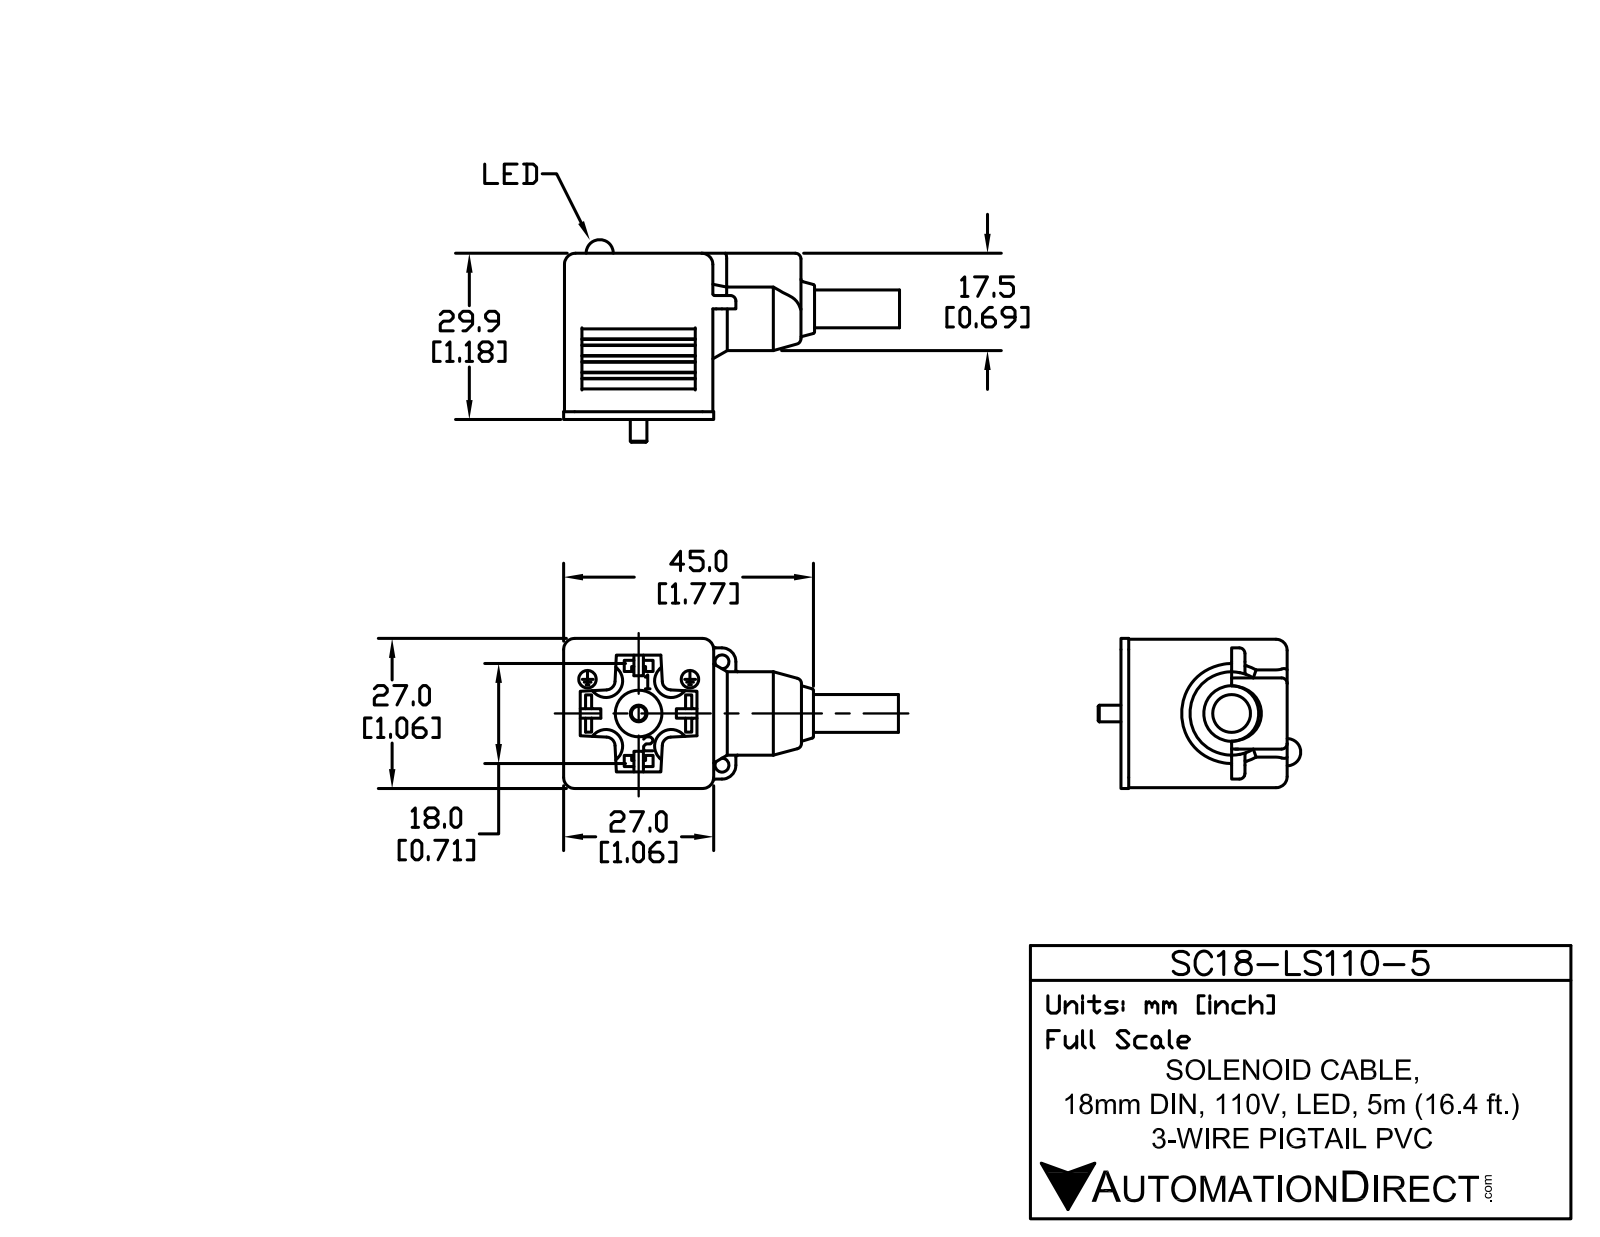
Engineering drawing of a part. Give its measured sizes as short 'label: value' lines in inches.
name: SC18-LS110-5
written by: SolidWorks 2011 (AUTOMOTIVE_DESIGN)
unit: in
bodies: 5 solids, 269 faces (210 planar, 34 cylindrical, 25 other)
size: 2.884 × 1.418 × 1.063
volume: 1.361 in³; area: 12.8 in²
holes: 2× ⌀0.089, 2× ⌀0.236, 1× ⌀0.157, 1× ⌀0.331
bosses: 1× ⌀0.226, 1× ⌀0.118, 1× ⌀0.108
rounds: 11× R0.039, 4× R0.079, 4× R0.118, 1× R0.295
face distances: 0.915, 1.063, 0.079, 0.994, 0.039, 0.876, 0.954, 1.051, 0.787, 0.276
hole spacings: 0.231, 0.232, 0.463
